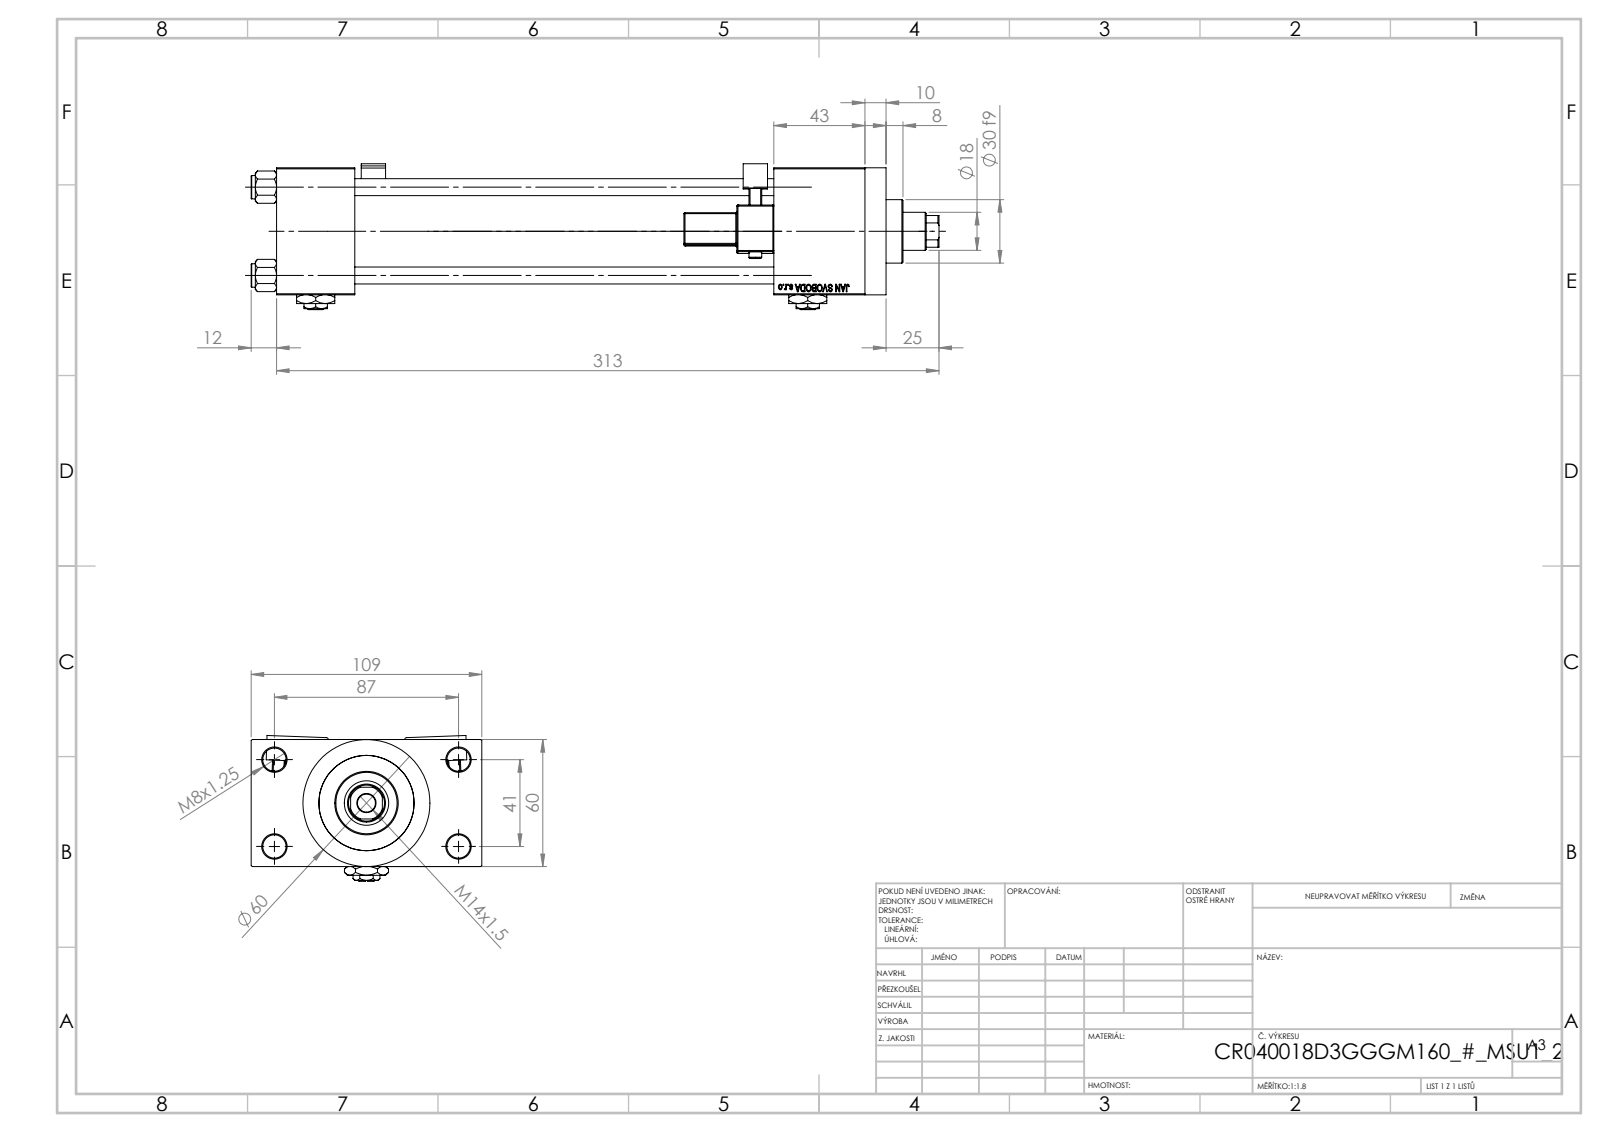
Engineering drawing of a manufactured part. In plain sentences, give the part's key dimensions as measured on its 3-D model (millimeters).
The part is named "NUT_M5_D; V215CR_MSU; V215CR_D_Body; V215CR_VCP_D (+3 more)". Its 3-D file was written by "SolidWorks 2019 (CONFIG_CONTROL_DESIGN)". It is 15 solids with 1360 faces: 604 planar, 160 cylindrical and 596 other. Overall it measures 325 by 109 by 68.9 millimeters. Its volume is 676 940 cubic millimeters and its surface area 195 818 square millimeters. Round holes: 4 of diameter 8, 4 of diameter 11, 2 of diameter 7, 2 of diameter 16.66, 2 of diameter 24, 1 of diameter 8.5, 1 of diameter 18, 1 of diameter 21, 1 of diameter 31, 1 of diameter 40, 1 of diameter 45. Round bosses or shafts: 4 of diameter 11, 2 of diameter 6, 1 of diameter 60, 1 of diameter 46, 1 of diameter 30. Partial cylindrical surfaces (rounded edges, fillets, slot ends): 48 of radius 0.5, 2 of radius 1, 2 of radius 2.5, 2 of radius 4, 1 of radius 8.5. The main face-to-face distances are 60, 198, 24.5, 84.5, 37, 235, 43, 278, 241, 109. The hole center spacings are 22.65, 29.49, 41.7, 47.15, 48.09, 64.35, 76.49, 41.
